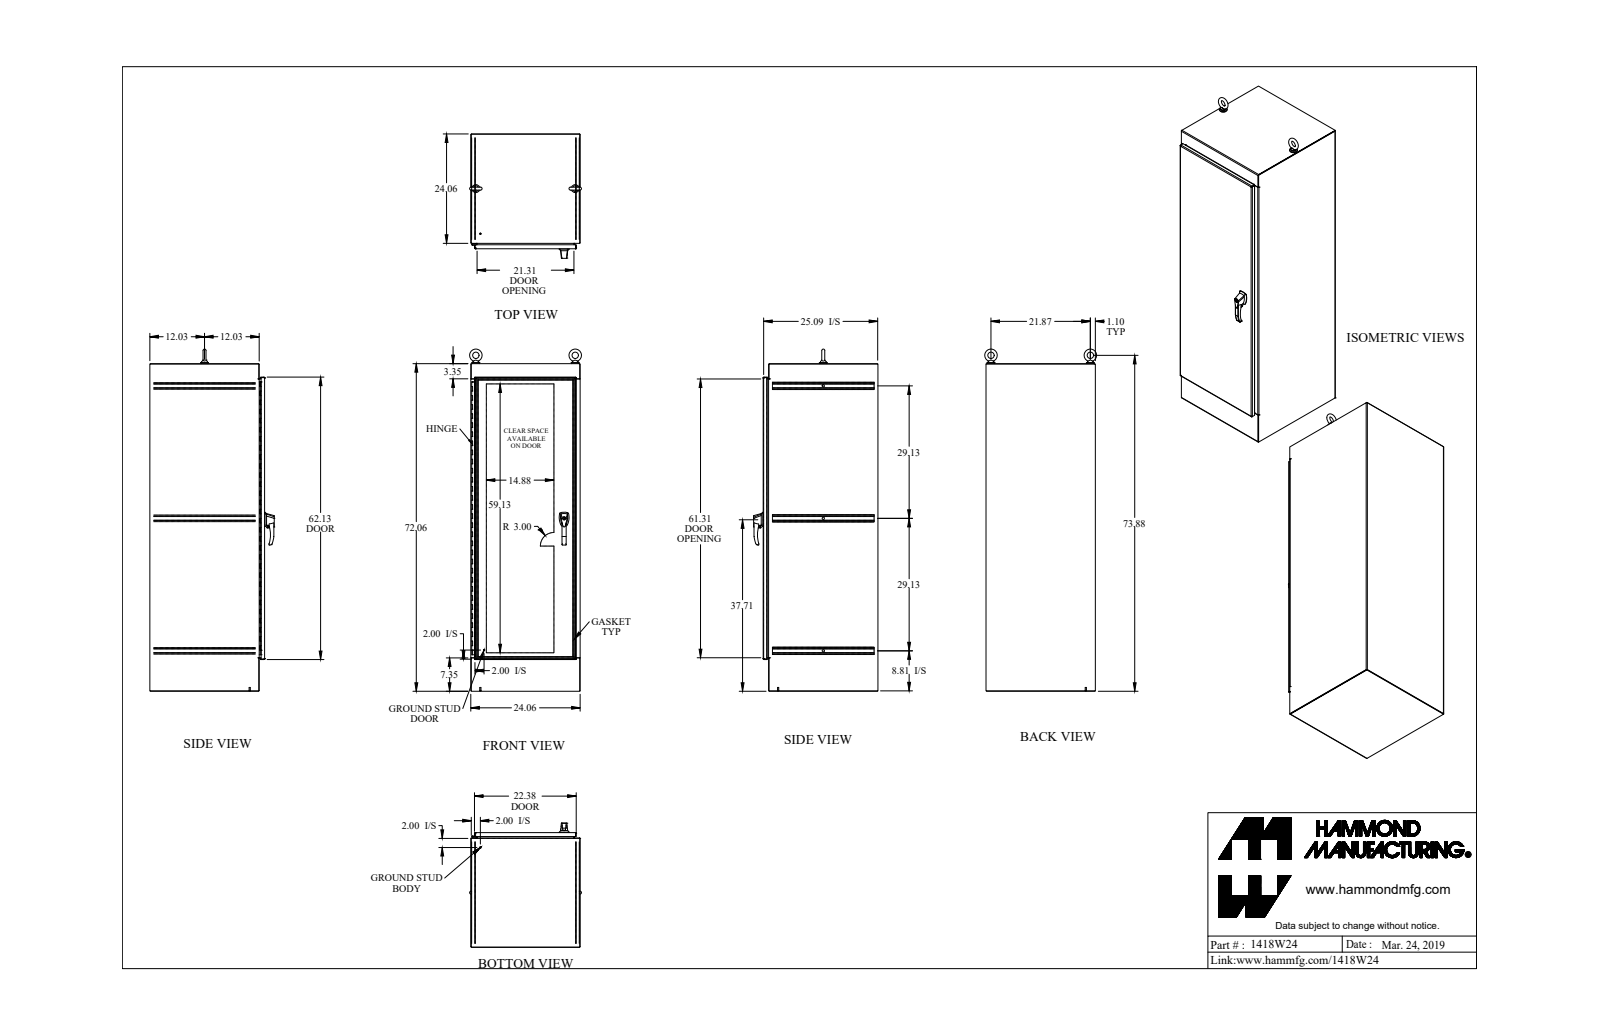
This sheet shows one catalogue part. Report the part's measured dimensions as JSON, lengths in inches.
{"part_name": "1418W24_Default", "step_written_by": "SolidWorks 2019 (CONFIG_CONTROL_DESIGN)", "units": "inches", "bodies": {"solids": 52, "faces": 1742, "planar": 781, "cylindrical": 796, "other": 165}, "overall_size": [75.713, 27.363, 25.118], "volume_in3": 930.8, "surface_area_in2": 19567, "round_holes": [[0.304, 10], [0.75, 4], [0.5, 3], [0.25, 2], [0.257, 2], [0.28, 2], [0.281, 2], [0.313, 2], [0.39, 2], [0.413, 2], [0.527, 2], [0.625, 2]], "round_bosses_or_shafts": [[0.281, 4], [1.75, 2], [1.5, 2], [1.25, 2], [1, 2], [0.75, 2], [0.738, 2], [0.63, 2]], "partial_cylinders_radius": [[0.043, 42], [0.138, 36], [0.125, 22], [0.018, 16], [0.048, 14], [0.143, 14], [0.06, 10], [0.318, 7]], "face_to_face_distances": [0.095, 23.965, 23.87, 0.095, 24.06, 25.057, 25.153, 25.152, 25.248, 71.965], "hole_center_spacings": [6, 12, 18, 24, 30, 21.87, 36, 42]}
